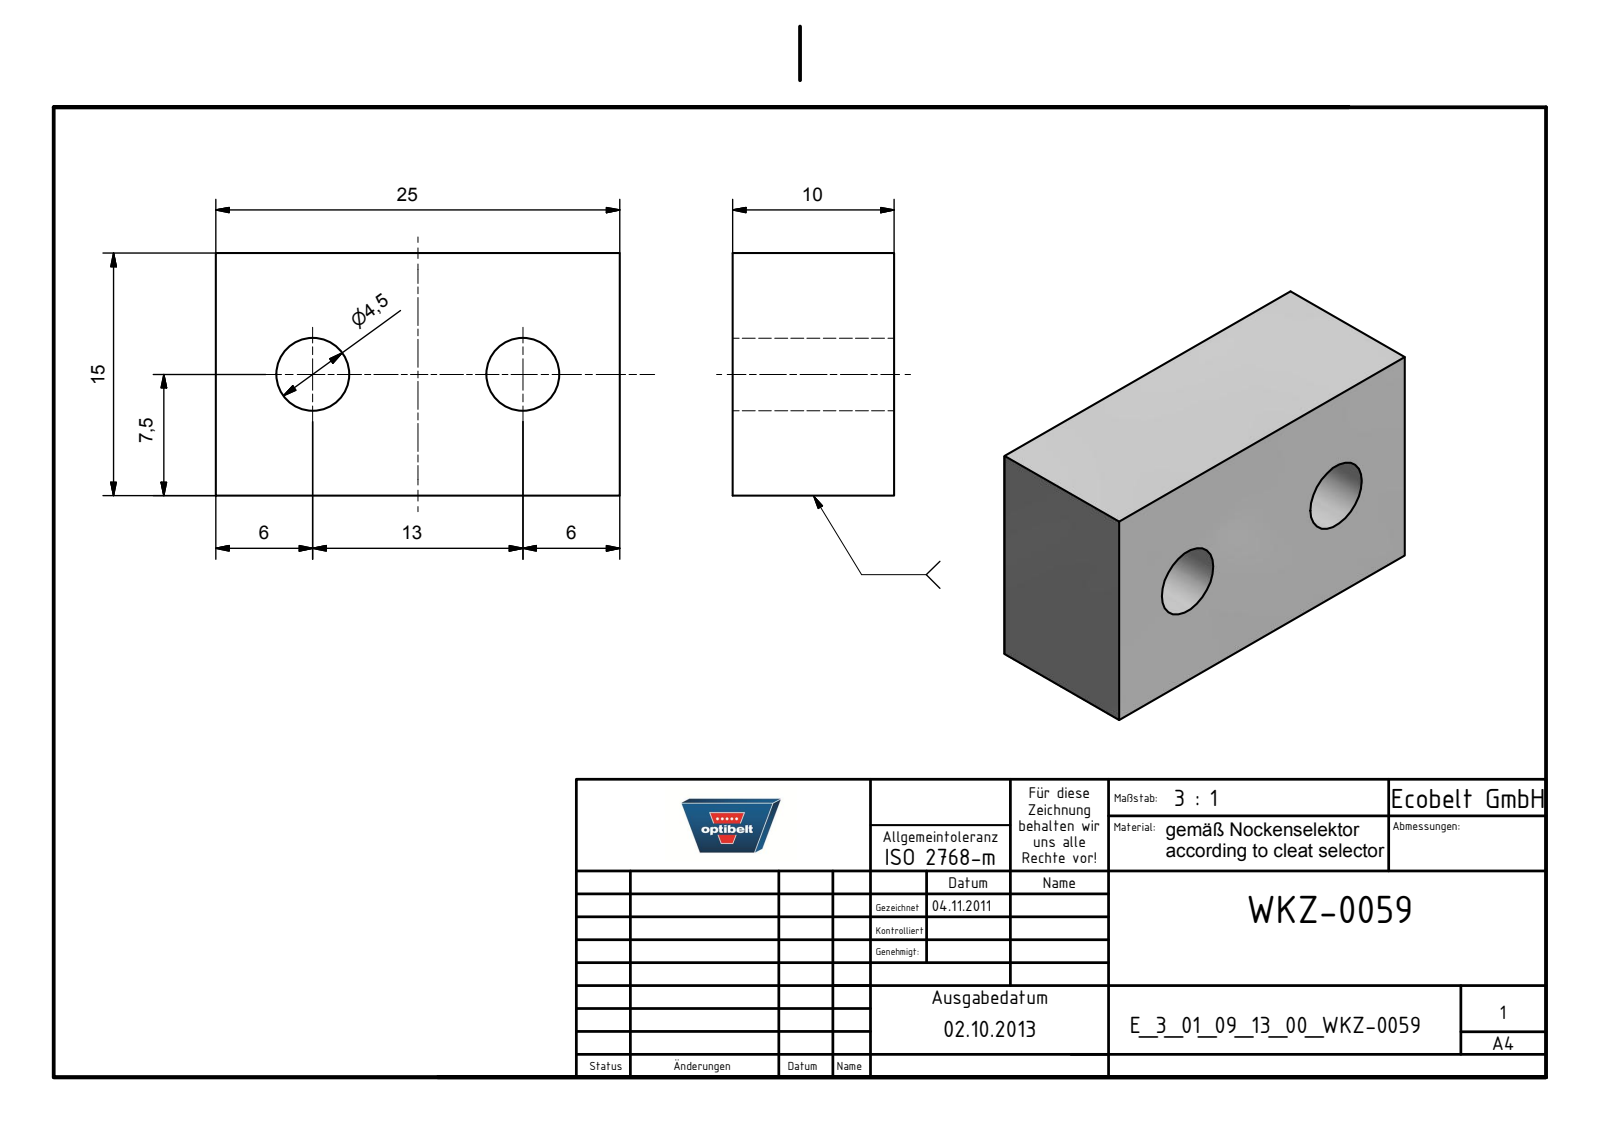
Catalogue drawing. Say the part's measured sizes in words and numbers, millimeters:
The part is named "E_3_01_09_13_00_WKZ-0059". Its 3-D file was written by "Autodesk Inventor 2025 (AUTOMOTIVE_DESIGN)". It is 1 solid with 8 faces: 6 planar, 2 cylindrical and 0 other. Overall it measures 25 by 15 by 10 millimeters. Its volume is 3 432 cubic millimeters and its surface area 1 769 square millimeters. Round holes: 2 of diameter 4.5. The main face-to-face distances are 10, 15, 25. The hole center spacings are 13.
